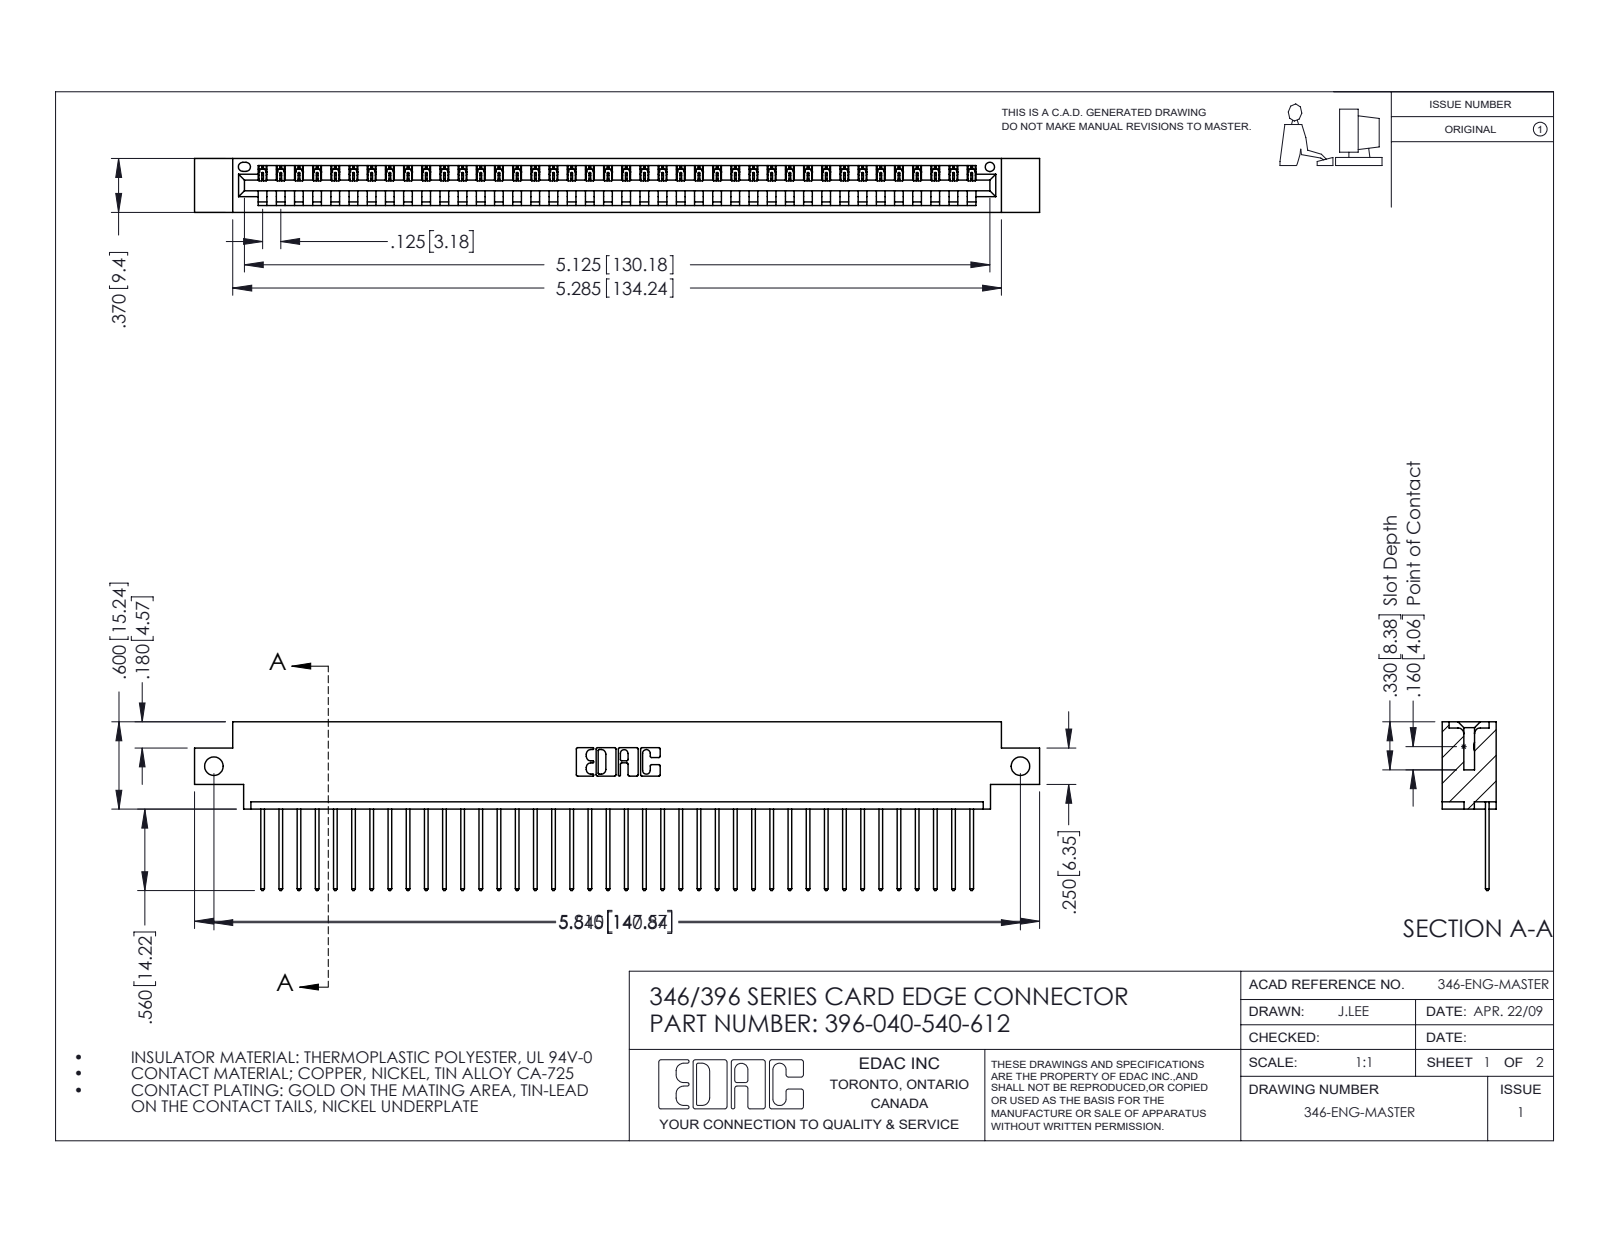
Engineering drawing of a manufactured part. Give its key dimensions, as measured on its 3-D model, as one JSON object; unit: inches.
{"part_name": "346 Part_0.170 Offset - Side Mount; 396-040-540-612; 345-292-001_345-293-140", "step_written_by": "SolidWorks 2016 (CONFIG_CONTROL_DESIGN)", "units": "inches", "bodies": {"solids": 41, "faces": 2446, "planar": 1680, "cylindrical": 766, "other": 0}, "overall_size": [5.81, 1.16, 0.37], "volume_in3": 0.85, "surface_area_in2": 27.58, "round_holes": [[0.128, 2], [0.064, 1]], "partial_cylinders_radius": [[0.006, 80], [0.01, 80], [0.01, 22], [0.007, 6], [0.031, 6], [0.026, 3], [0.031, 2], [0.04, 2]], "face_to_face_distances": [0.048, 0.322, 0.37, 0.25, 0.072, 0.298, 0.025, 0.148, 0.222, 0.1], "hole_center_spacings": [5.545]}
